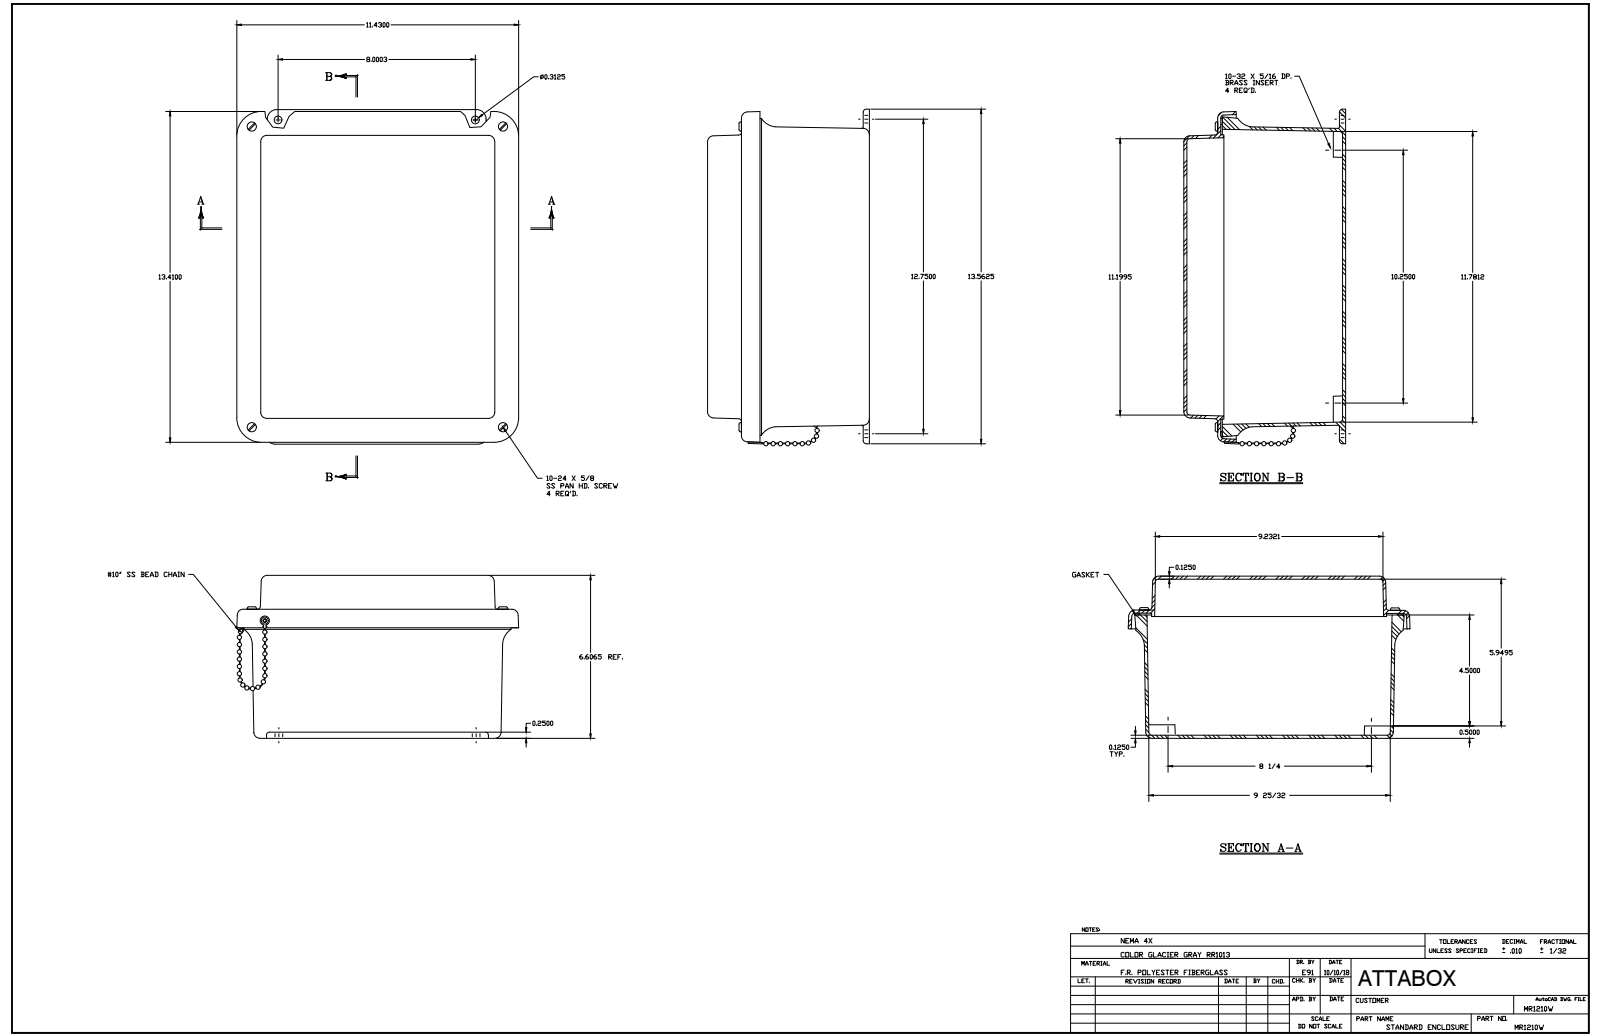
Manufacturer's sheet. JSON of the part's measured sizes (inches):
{"part_name": "MR1210W", "step_written_by": "SolidWorks 2018 (AUTOMOTIVE_DESIGN)", "units": "inches", "bodies": {"solids": 45, "faces": 937, "planar": 210, "cylindrical": 299, "other": 428}, "overall_size": [14.029, 11.676, 6.576], "volume_in3": 91.01, "surface_area_in2": 1245, "round_holes": [[0.14, 5], [0.152, 5], [0.145, 4], [0.156, 4], [0.218, 4], [0.187, 2], [0.126, 1]], "round_bosses_or_shafts": [[0.27, 8], [0.19, 4], [0.156, 4], [0.375, 2], [0.25, 2], [0.283, 1], [0.125, 1], [0.125, 1]], "partial_cylinders_radius": [[0.031, 20], [0.125, 20], [0.25, 12], [0.2, 4], [0.285, 4], [0.313, 4], [0.375, 4], [0.75, 4]], "face_to_face_distances": [0.125, 0.125, 6.326, 6.576, 6.451, 6.451, 1.387, 4.939, 5.064, 1.512], "hole_center_spacings": [1.348, 9.252, 11.243, 14.498, 3.625, 6.875, 8.25, 10.156]}
